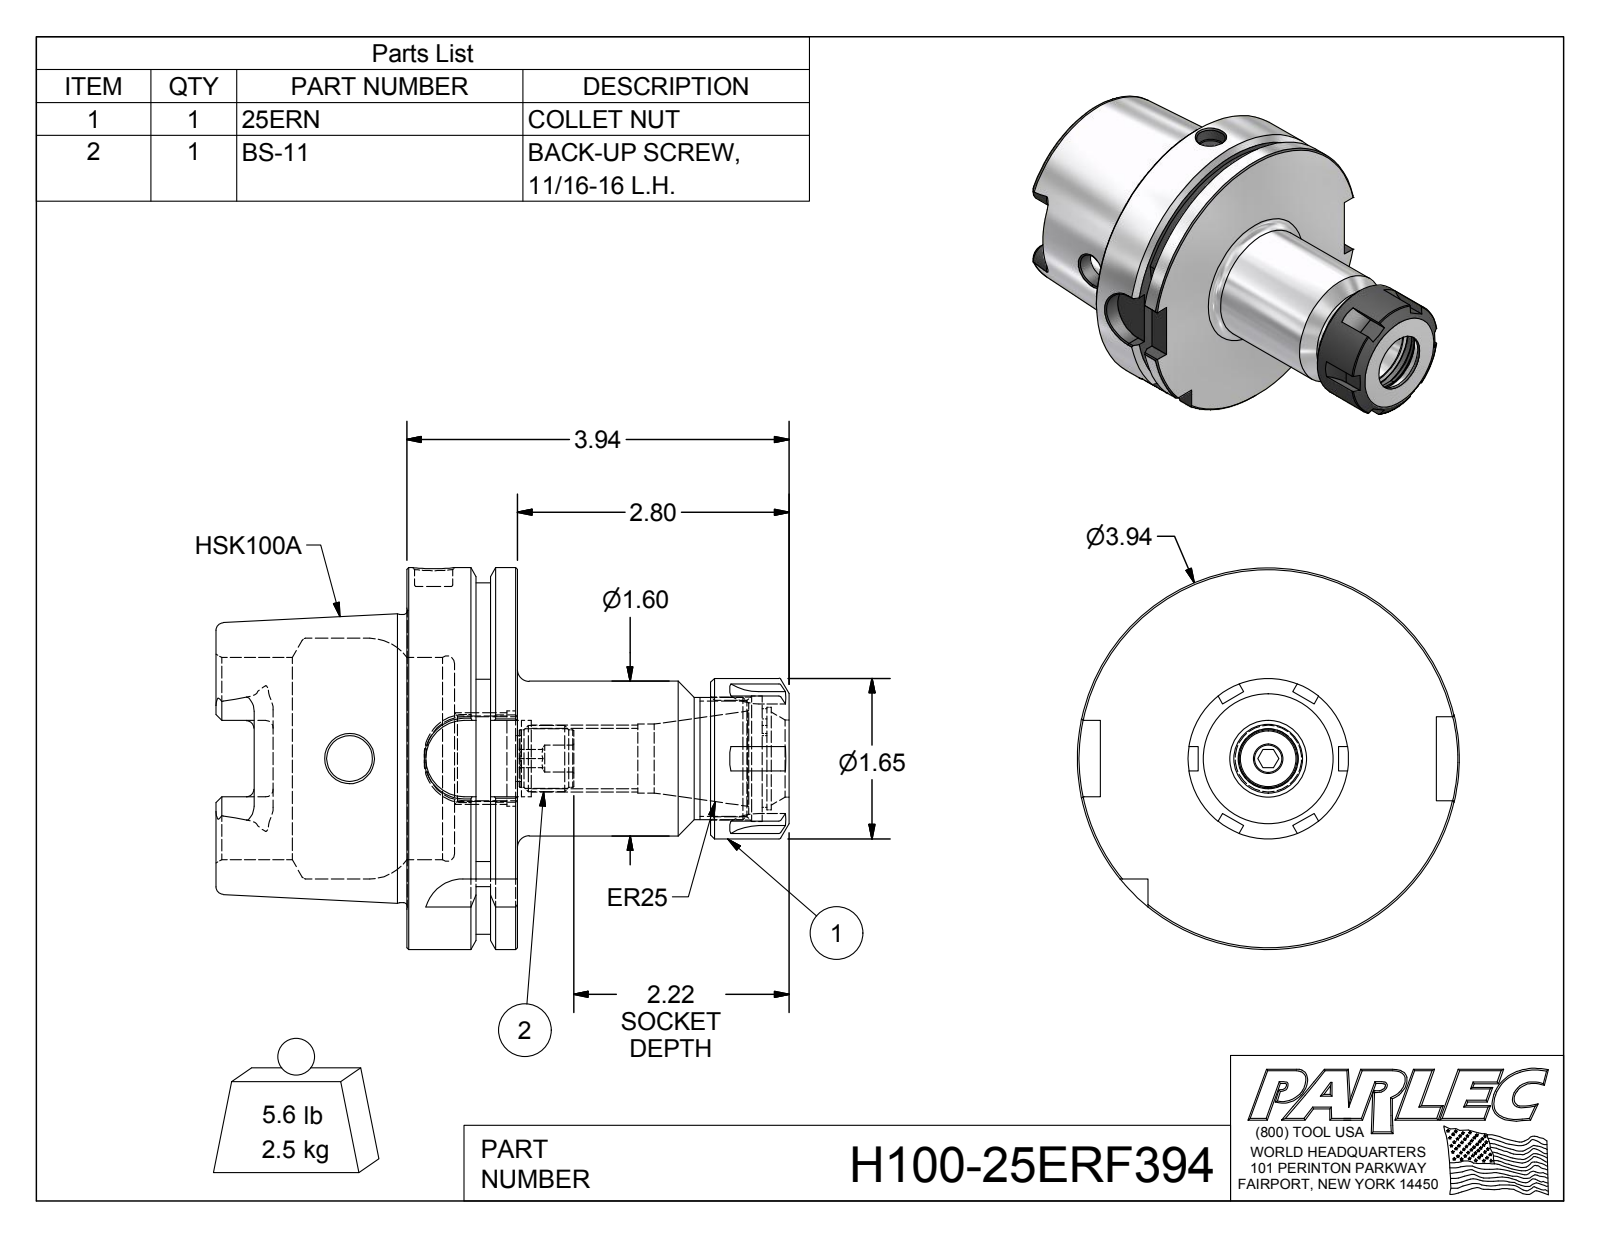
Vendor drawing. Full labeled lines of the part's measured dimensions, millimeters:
Part name (STEP PRODUCT): H100-25ERF394; H100-25ER4-1; 25ERN; BS-11
STEP written by: Autodesk Inventor 2012 (AUTOMOTIVE_DESIGN)
Units: millimetres
Bodies: 3 solids, 206 faces (82 planar, 57 cylindrical, 67 other)
Overall size (bounding box): 150.1 × 100 × 100
Volume: 323 500 mm³ · Surface area: 68 190 mm²
Round holes (diameter × count): ⌀12 ×2, ⌀7.1 ×1, ⌀10 ×1, ⌀12 ×1, ⌀15.7 ×1, ⌀18 ×1, ⌀19.9 ×1, ⌀20.2 ×1, ⌀22.4 ×1, ⌀25 ×1, ⌀26.8 ×1, ⌀30.5 ×1
Round bosses / shafts (diameter × count): ⌀100 ×1, ⌀75.4 ×1, ⌀42 ×1, ⌀40.5 ×1, ⌀32 ×1, ⌀17.3 ×1, ⌀15.1 ×1
Partial cylindrical surfaces — rounded edges, fillets, slot ends (radius × count): R2 ×6, R12.7 ×6, R4.9 ×4, R10 ×4, R12 ×1, R13.1 ×1, R46 ×1
Main face-to-face distances: 29, 12.5, 16.5, 50, 62.5, 79, 150.1, 100.1, 87.6, 71.1
